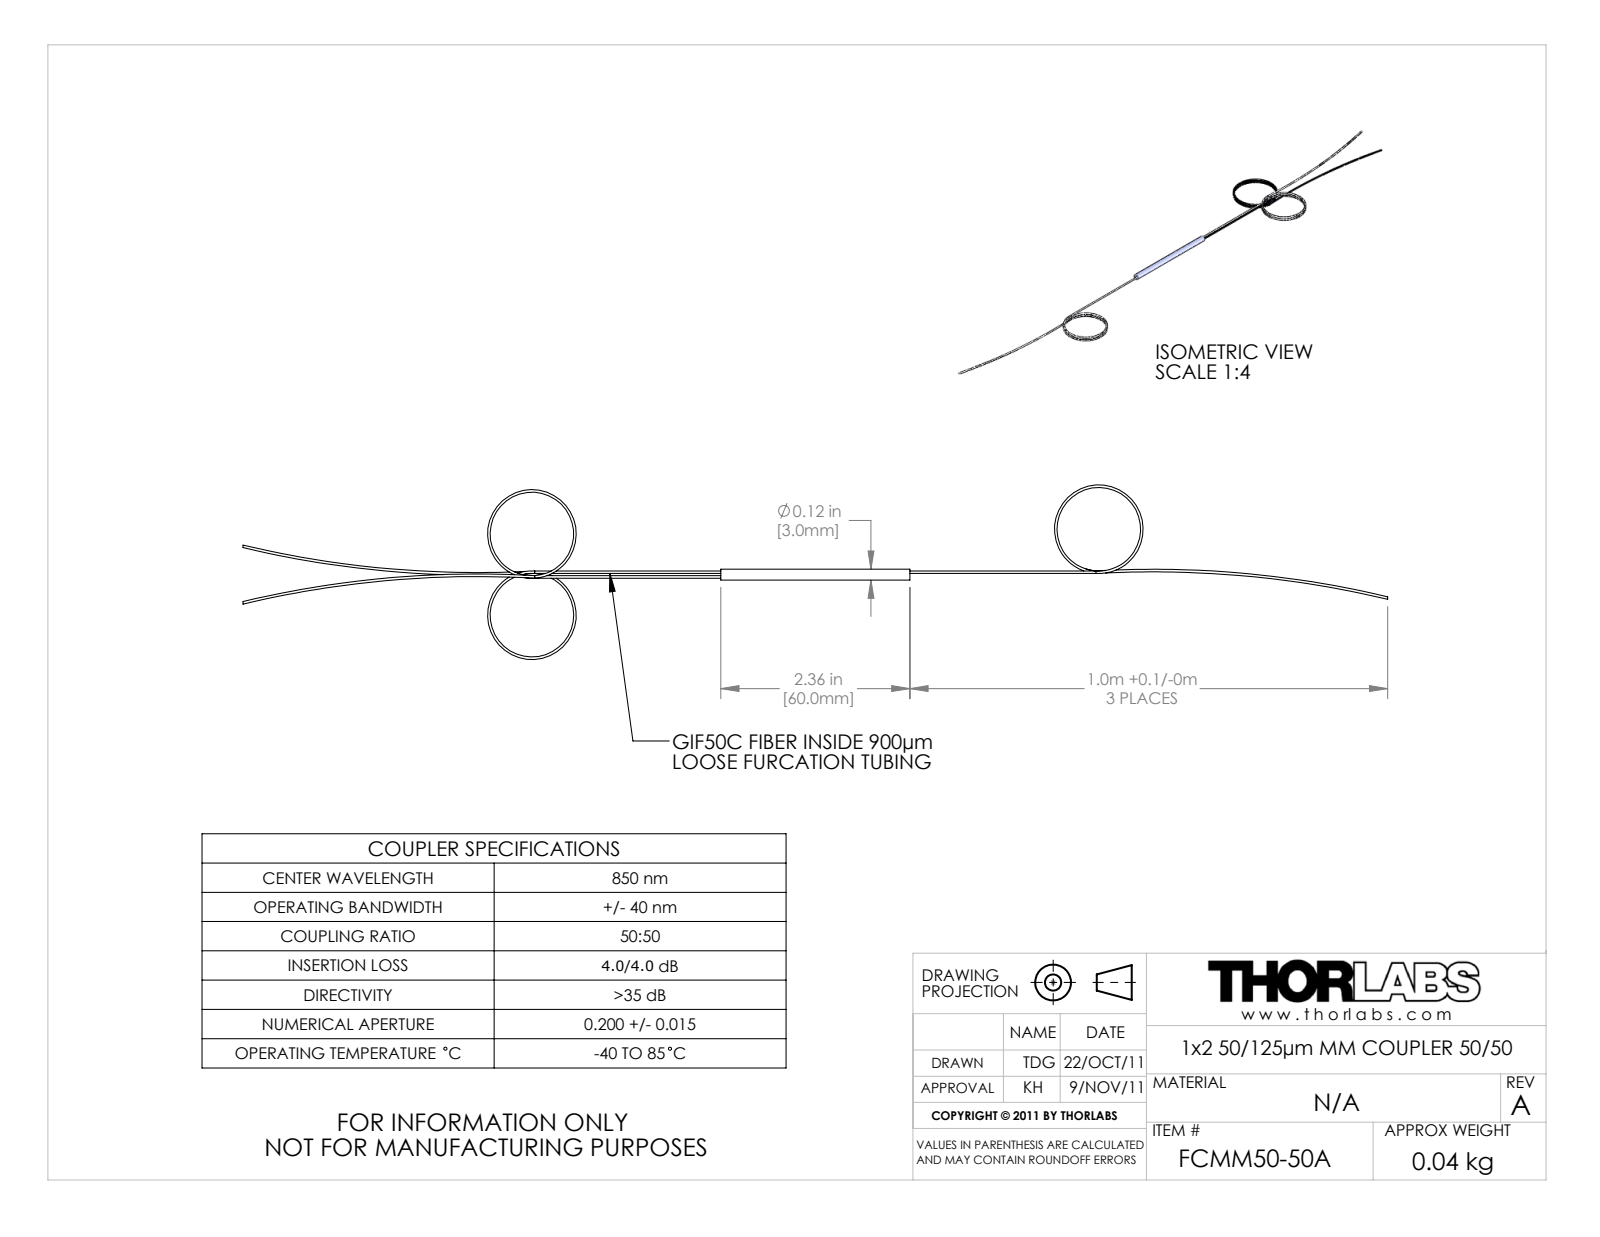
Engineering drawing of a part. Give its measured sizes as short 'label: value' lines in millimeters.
name: 13895-E0W
written by: SolidWorks 2011 (AUTOMOTIVE_DESIGN)
unit: mm
bodies: 4 solids, 46 faces (10 planar, 18 cylindrical, 18 other)
size: 399.8 × 61 × 6.9
volume: 1 100 mm³; area: 5 627 mm²
holes: 2× ⌀1, 1× ⌀3.3
bosses: 2× ⌀0.9, 1× ⌀3.8
face distances: 65.9, 66, 65.8, 166.9, 167, 232.8, 232.9, 201.9, 31, 35
hole spacings: 0.8, 1.7
